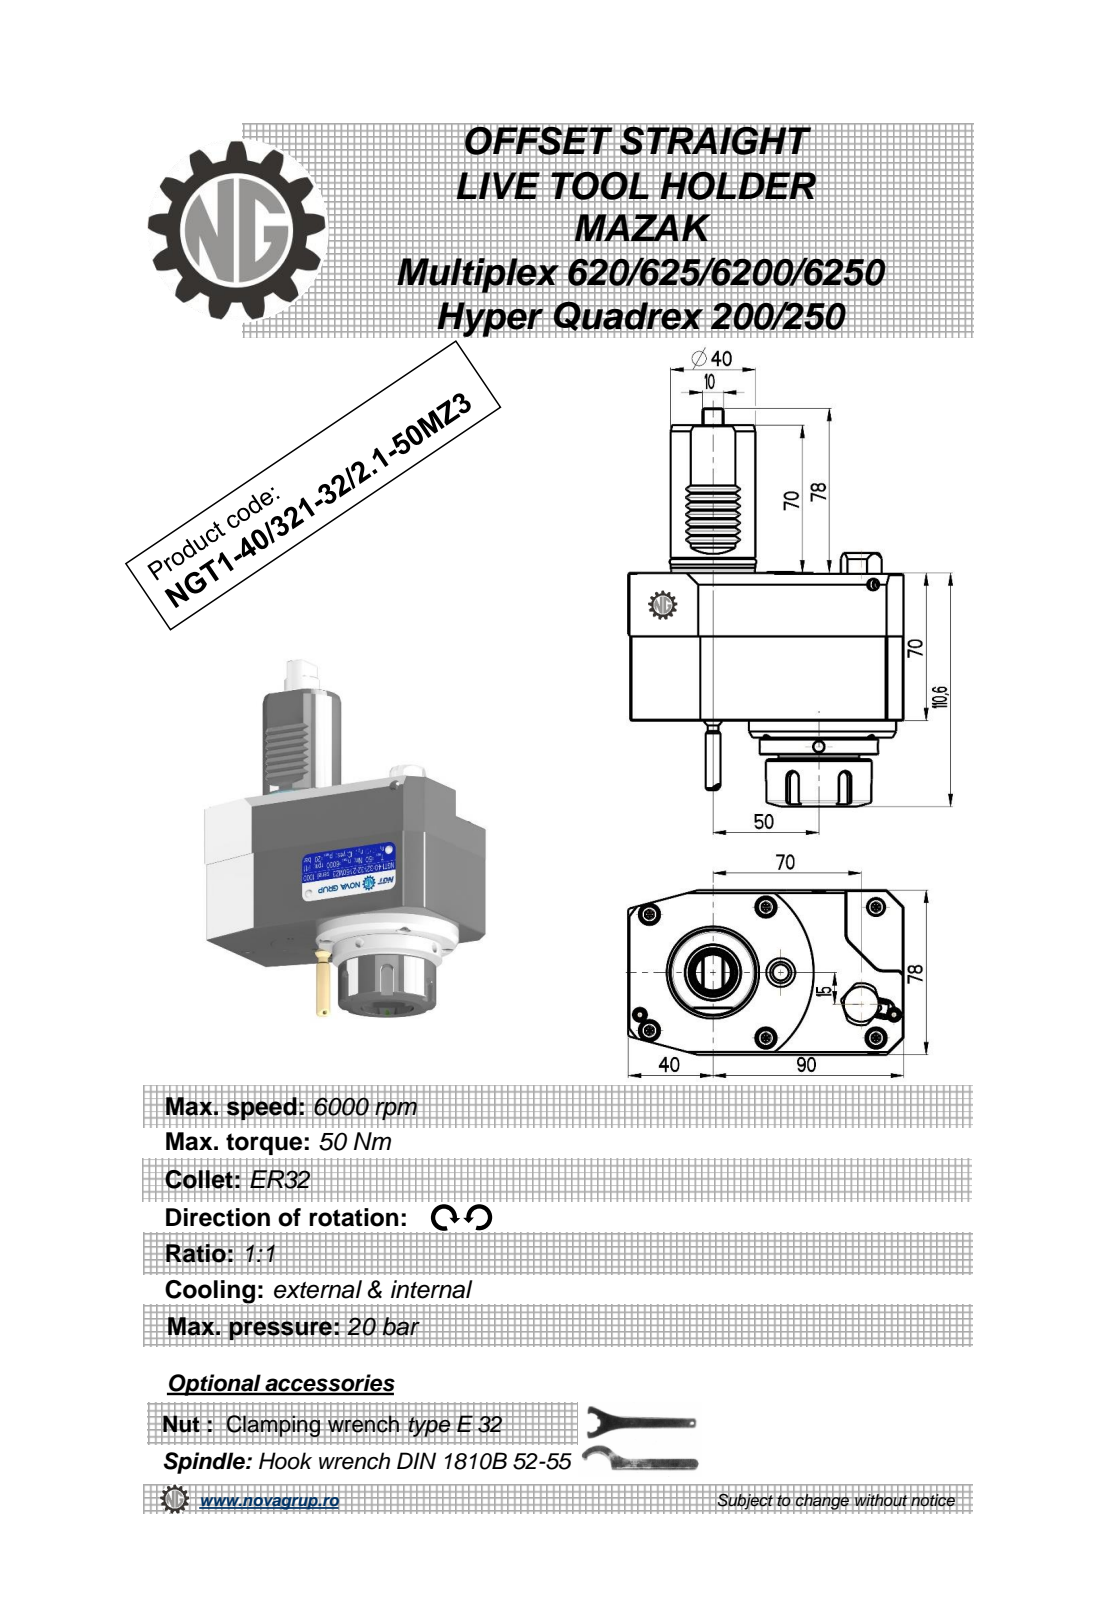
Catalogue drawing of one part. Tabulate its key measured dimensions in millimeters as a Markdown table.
| quantity | value |
| --- | --- |
| part name | NGT1_40_221_32_1_2_130MZ3 |
| STEP written by | PRO/ENGINEER BY PARAMETRIC TECHNOLOGY CORPORATION, 2010280 (CONFIG_CONTROL_DESIGN) |
| units | millimeters |
| bodies | 1 solid, 270 faces (117 planar, 68 cylindrical, 85 other) |
| overall size | 188.6 × 130 × 78 |
| volume | 849 781 mm³ |
| surface area | 69 608 mm² |
| round holes (diameter × count) | 5 × 2, 2.5 × 1, 3 × 1, 7.5 × 1, 27 × 1 |
| round bosses / shafts (diameter × count) | 73 × 1, 56 × 1, 50 × 1, 42 × 1, 41 × 1, 40 × 1, 39.4 × 1, 36.2 × 1 |
| partial cylindrical surfaces (radius × count) | 0.3 × 7, 0.16 × 6, 3 × 5, 10 × 3, 0.8 × 2, 9 × 1 |
| main face-to-face distances | 78, 70, 8, 129, 1, 130, 56, 16, 86, 64 |
| hole center spacings | 18, 38.55, 54.43 |
